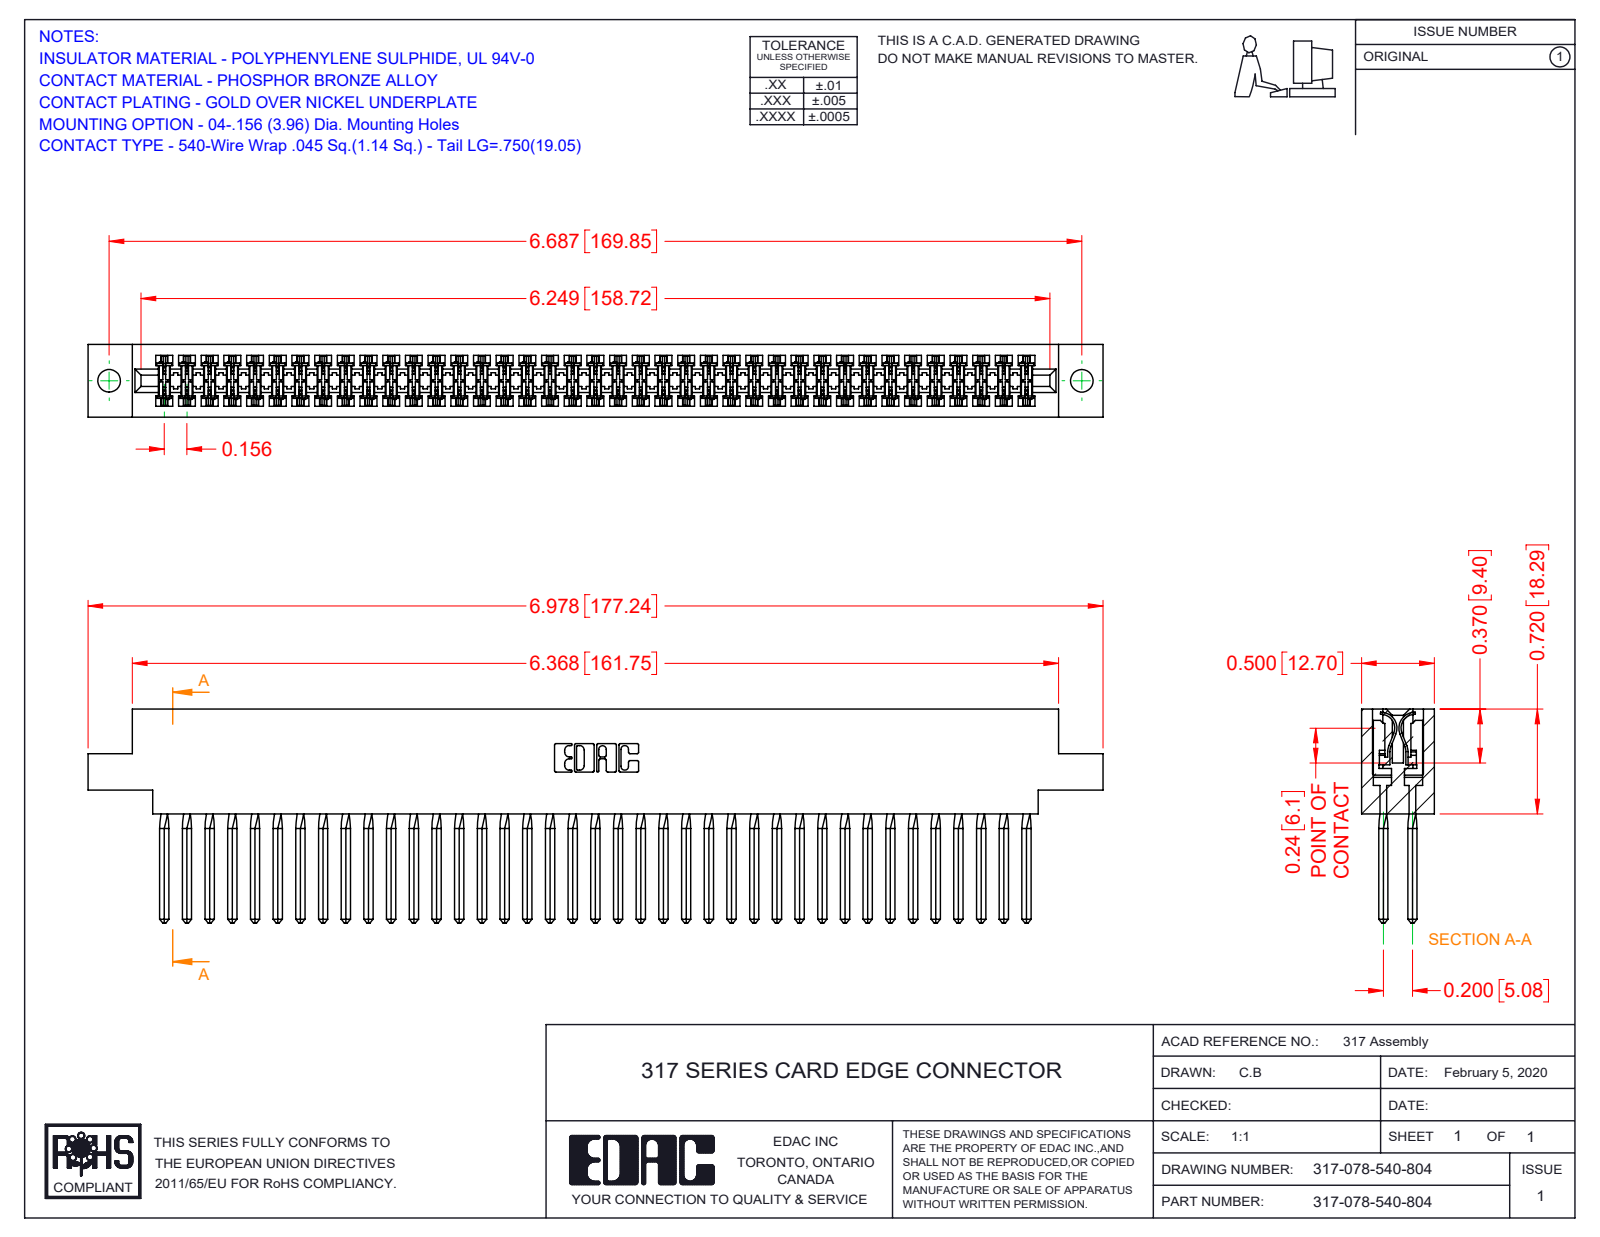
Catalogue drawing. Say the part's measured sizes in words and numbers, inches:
The part is named "317-290-001_540; 317 Part_.156 Dia - TH; 317-078-540-804". Its 3-D file was written by "SolidWorks 2016 (CONFIG_CONTROL_DESIGN)". It is 79 solids with 7044 faces: 5752 planar, 980 cylindrical and 312 other. Overall it measures 6.978 by 1.47 by 0.5 inches. Its volume is 1.804 cubic inches and its surface area 67.86 square inches. Round holes: 2 of diameter 0.156. Partial cylindrical surfaces (rounded edges, fillets, slot ends): 156 of radius 0.015, 22 of radius 0.01, 6 of radius 0.007, 6 of radius 0.031, 3 of radius 0.026, 2 of radius 0.095, 2 of radius 0.1, 2 of radius 0.11. The main face-to-face distances are 0.5, 0.075, 0.425, 0.35, 0.195, 0.094, 0.2, 0.115, 0.131, 0.11. The hole center spacings are 6.687.
